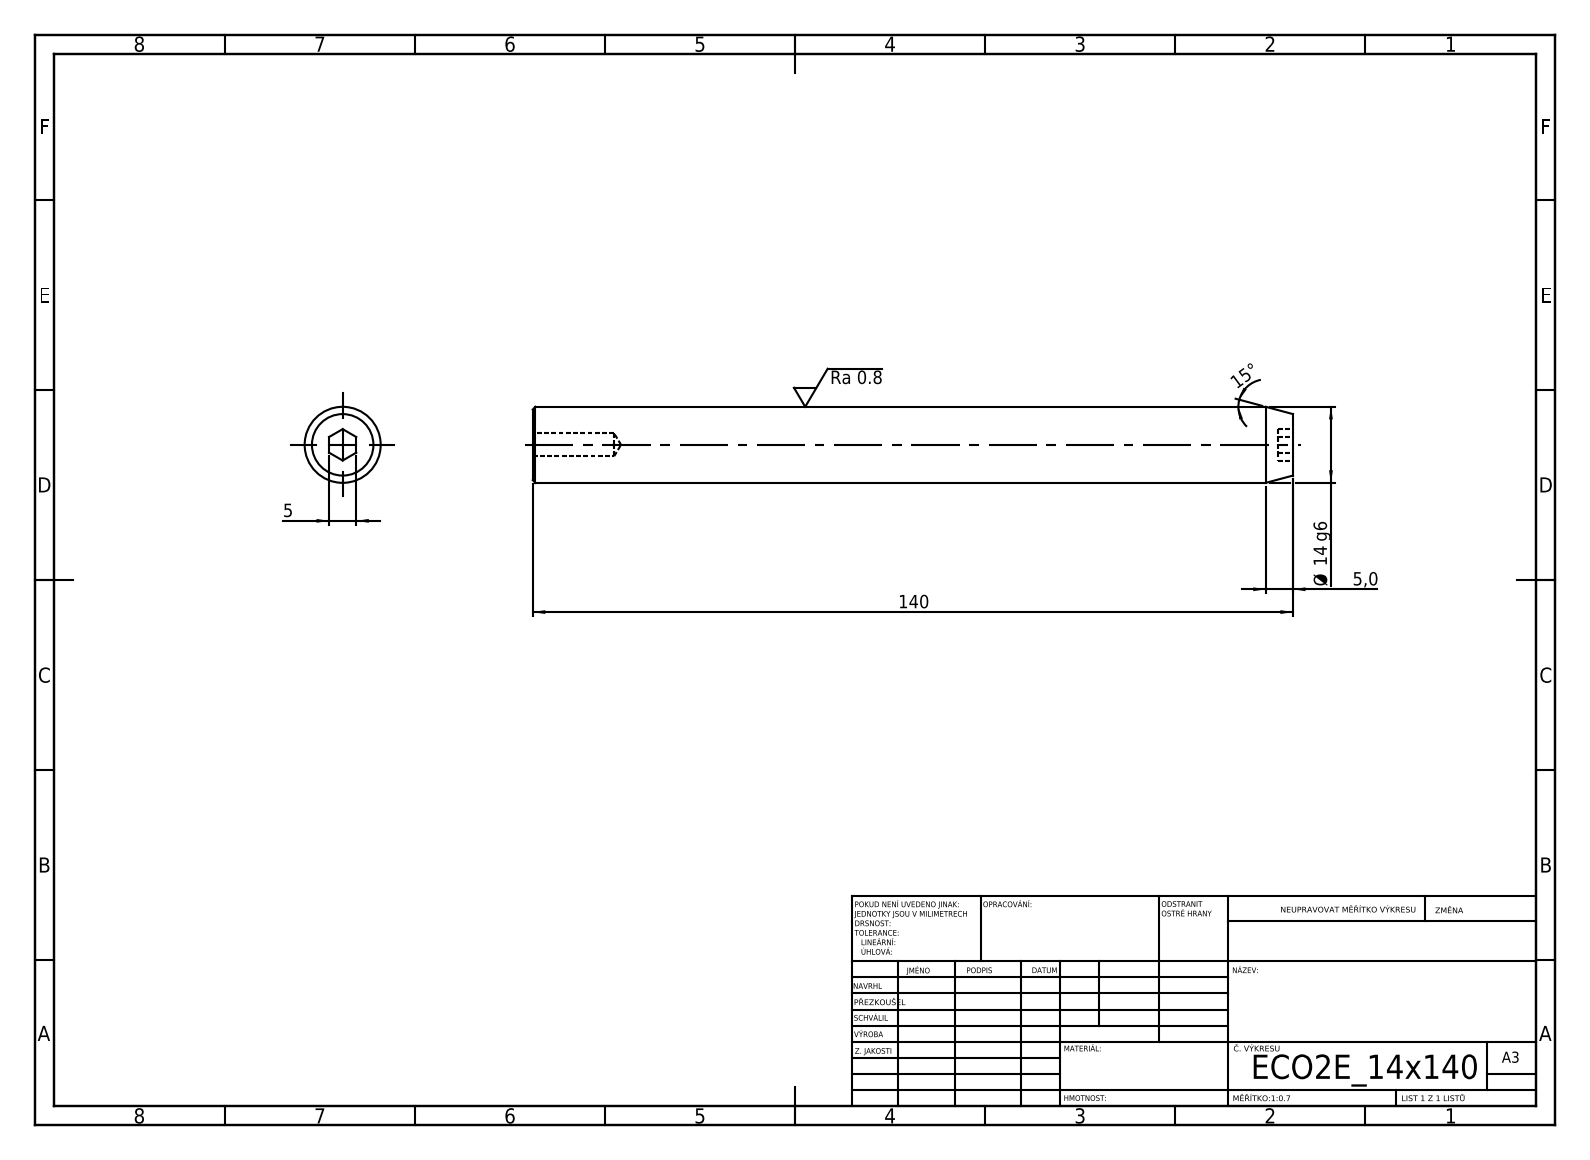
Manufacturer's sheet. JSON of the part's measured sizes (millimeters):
{"step_written_by": "SolidWorks 2019 (CONFIG_CONTROL_DESIGN)", "units": "millimeters", "bodies": {"solids": 1, "faces": 19, "planar": 9, "cylindrical": 4, "other": 6}, "overall_size": [140, 14, 14], "volume_mm3": 21134, "surface_area_mm2": 6634, "round_holes": [[4.2, 1]], "round_bosses_or_shafts": [[14, 1]], "face_to_face_distances": [140, 5, 2.8, 137.2]}
